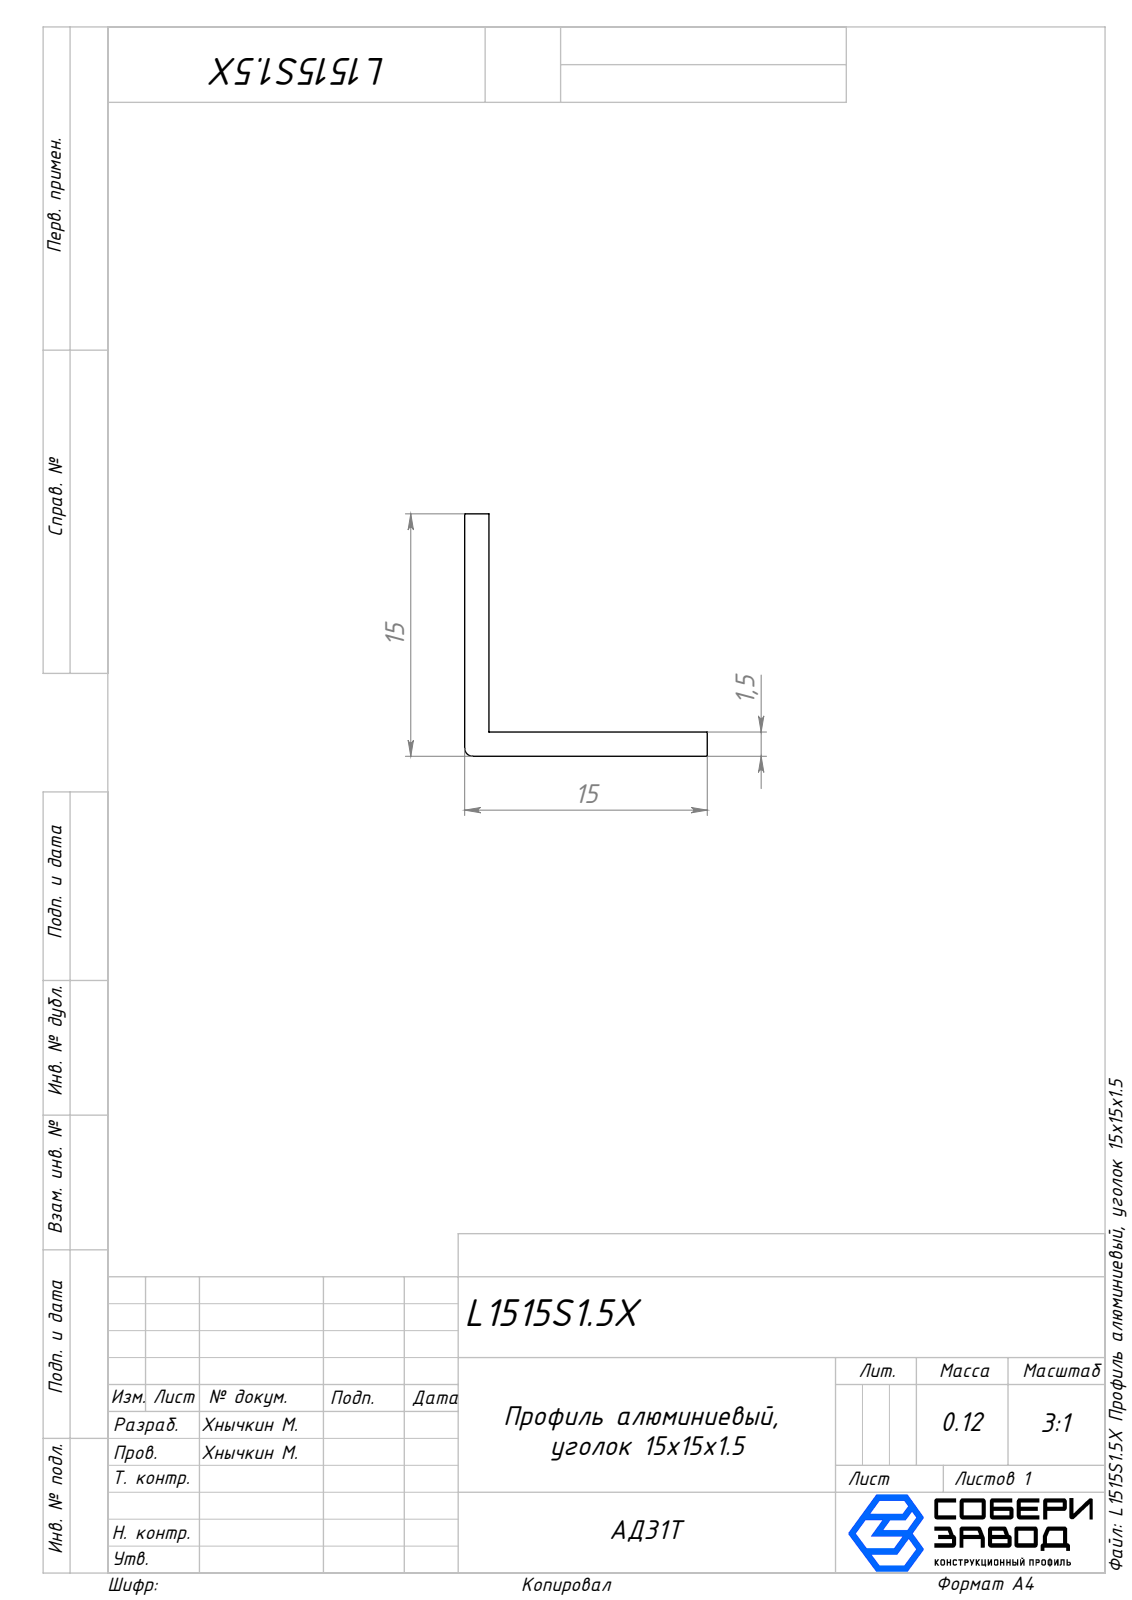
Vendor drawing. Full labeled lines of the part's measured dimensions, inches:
Part name (STEP PRODUCT): L1515S1.5X Профиль алюминиевый, уголок 15х15х1.5
STEP written by: SolidWorks 2025 (AUTOMOTIVE_DESIGN)
Units: inches
Bodies: 1 solid, 9 faces (8 planar, 1 cylindrical, 0 other)
Overall size (bounding box): 39.37 × 0.591 × 0.591
Volume: 2.605 in³ · Surface area: 92.8 in²
Partial cylindrical surfaces — rounded edges, fillets, slot ends (radius × count): R0.02 ×1
Main face-to-face distances: 0.059, 0.591, 0.531, 39.37
